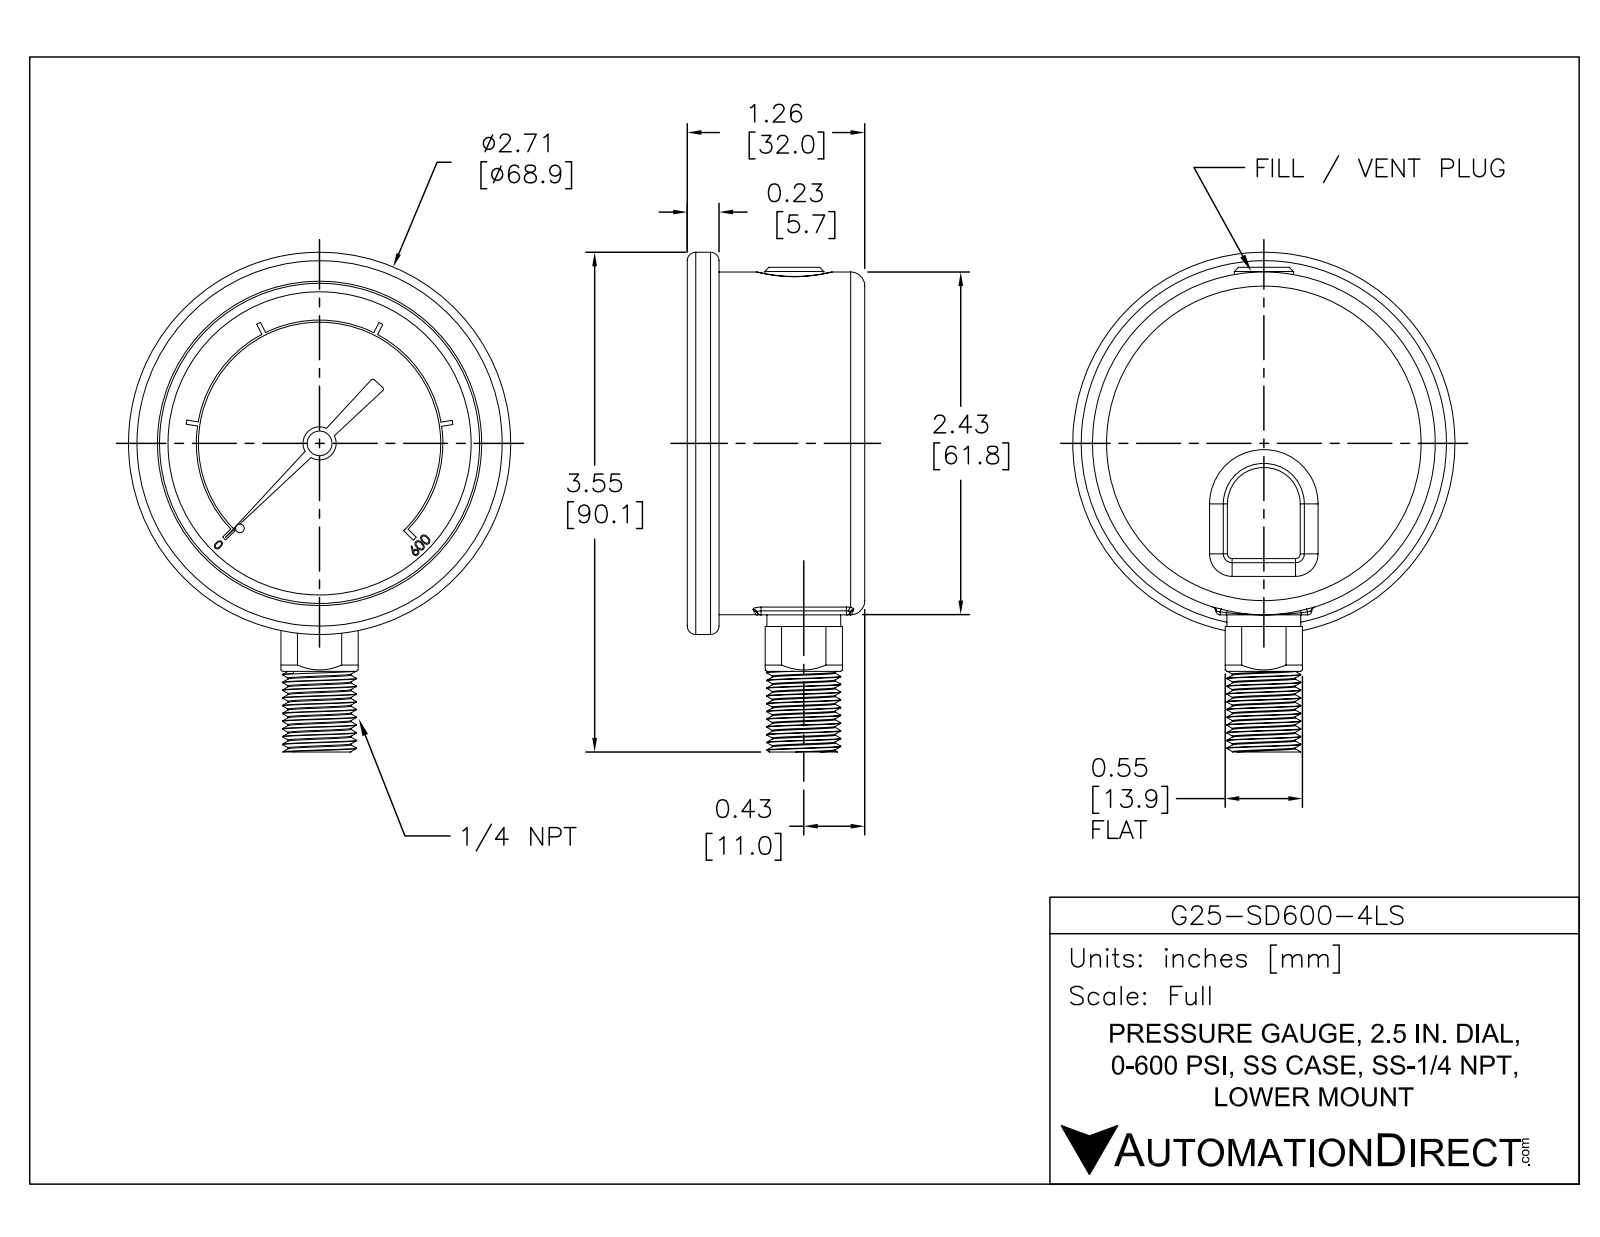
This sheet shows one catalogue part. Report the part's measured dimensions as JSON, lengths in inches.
{"part_name": "G25-SD600-4LS", "step_written_by": "SolidWorks 2021 (AUTOMOTIVE_DESIGN)", "units": "inches", "bodies": {"solids": 1, "faces": 350, "planar": 193, "cylindrical": 85, "other": 72}, "overall_size": [3.546, 2.713, 1.26], "volume_in3": 5.273, "surface_area_in2": 24.68, "round_holes": [[0.027, 1], [0.071, 1], [0.119, 1], [2.272, 1]], "round_bosses_or_shafts": [[2.713, 1], [2.433, 1], [0.524, 1], [0.42, 1], [0.235, 1], [0.176, 1], [0.14, 1], [0.041, 1]], "partial_cylinders_radius": [[0.03, 9], [0.1, 3], [0.015, 2], [0.316, 1], [0.86, 1], [0.875, 1]], "face_to_face_distances": [1.01, 1.26, 0.25, 1.035, 0.025, 0.225, 0.1, 0.91, 0.935, 1.16], "hole_center_spacings": [0.067]}
